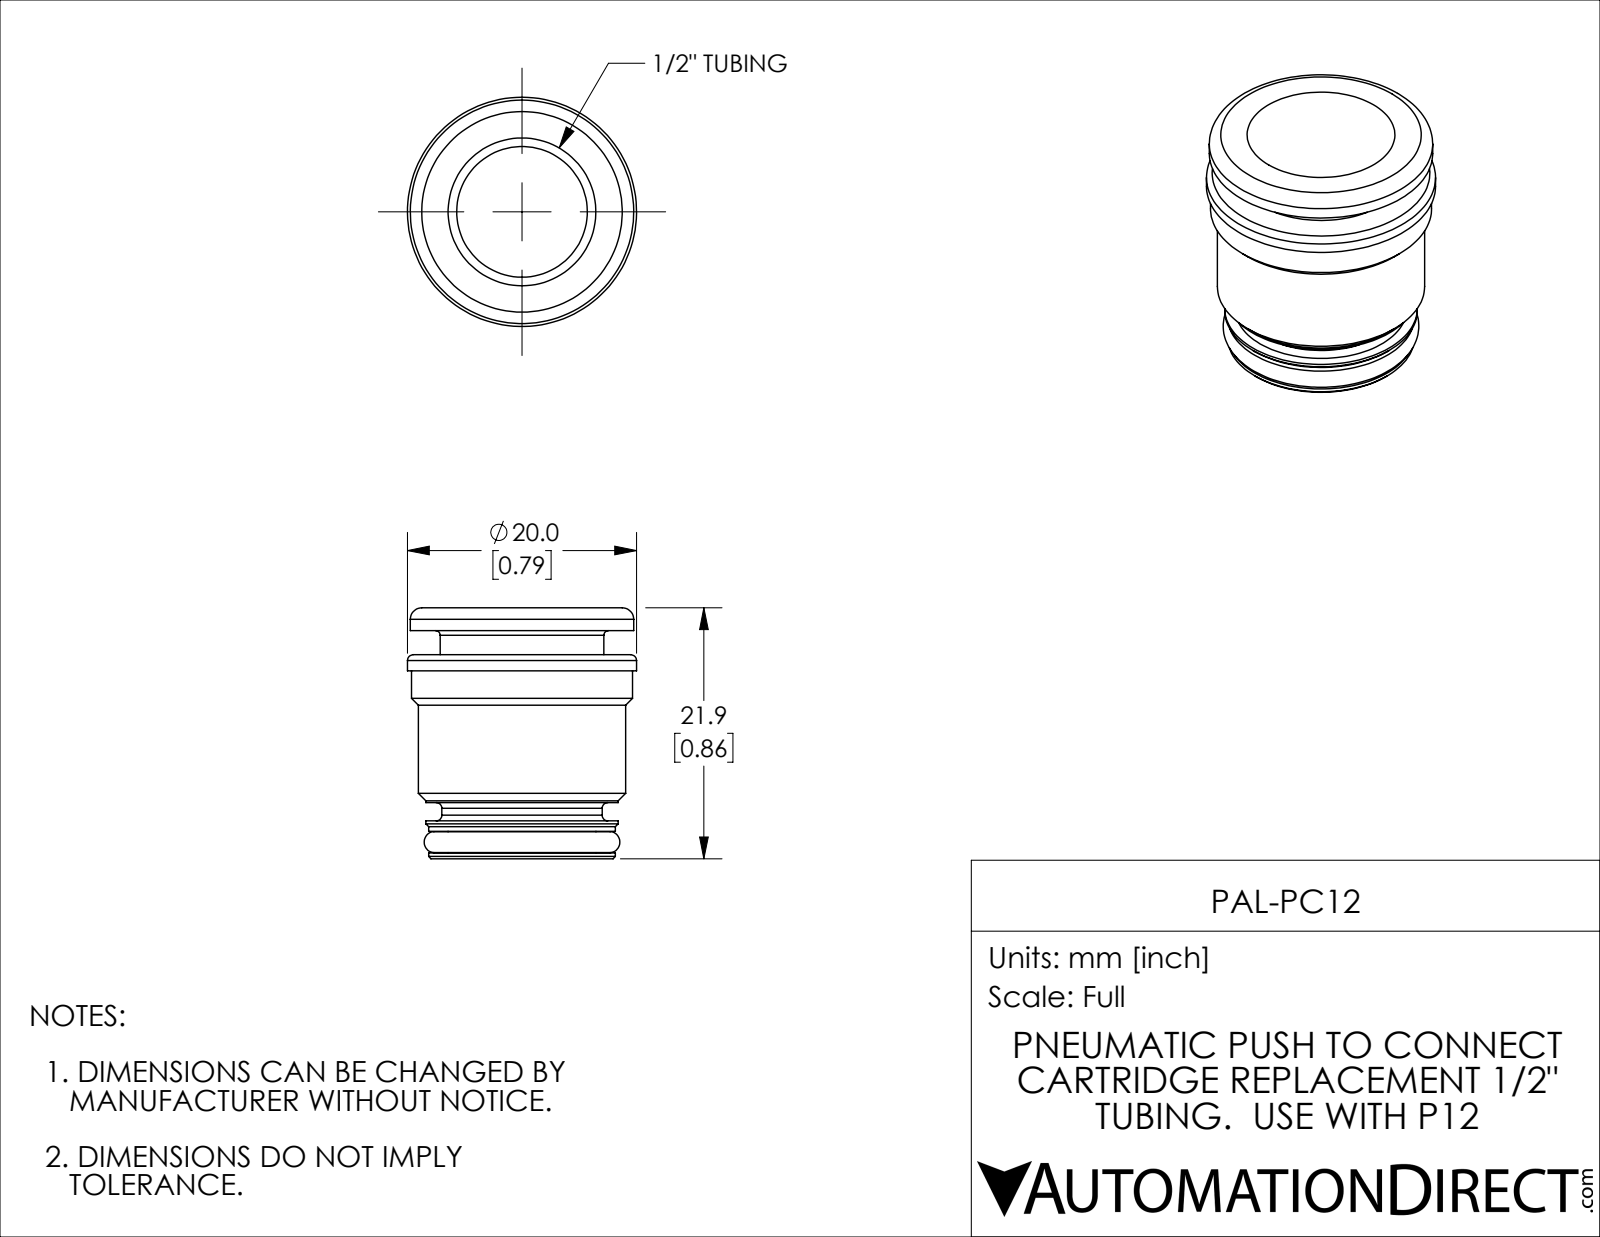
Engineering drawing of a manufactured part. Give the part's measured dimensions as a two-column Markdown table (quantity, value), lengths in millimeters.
| quantity | value |
| --- | --- |
| part name | PAL-PC12 |
| STEP written by | SolidWorks 2019 (CONFIG_CONTROL_DESIGN) |
| units | millimeters |
| bodies | 2 solids, 58 faces (10 planar, 26 cylindrical, 22 other) |
| overall size | 21.9 × 20 × 20 |
| volume | 2 559 mm³ |
| surface area | 3 193 mm² |
| round holes (diameter × count) | 11.4 × 1, 12.9 × 1 |
| round bosses / shafts (diameter × count) | 20 × 1, 19.5 × 1, 19.3 × 1, 18.1 × 1, 16.8 × 1, 16.3 × 1, 14.3 × 1, 14 × 1 |
| main face-to-face distances | 2.1, 4.1, 2, 17.8, 19.9, 21.9, 2.4, 15.4, 17.5, 19.5 |
